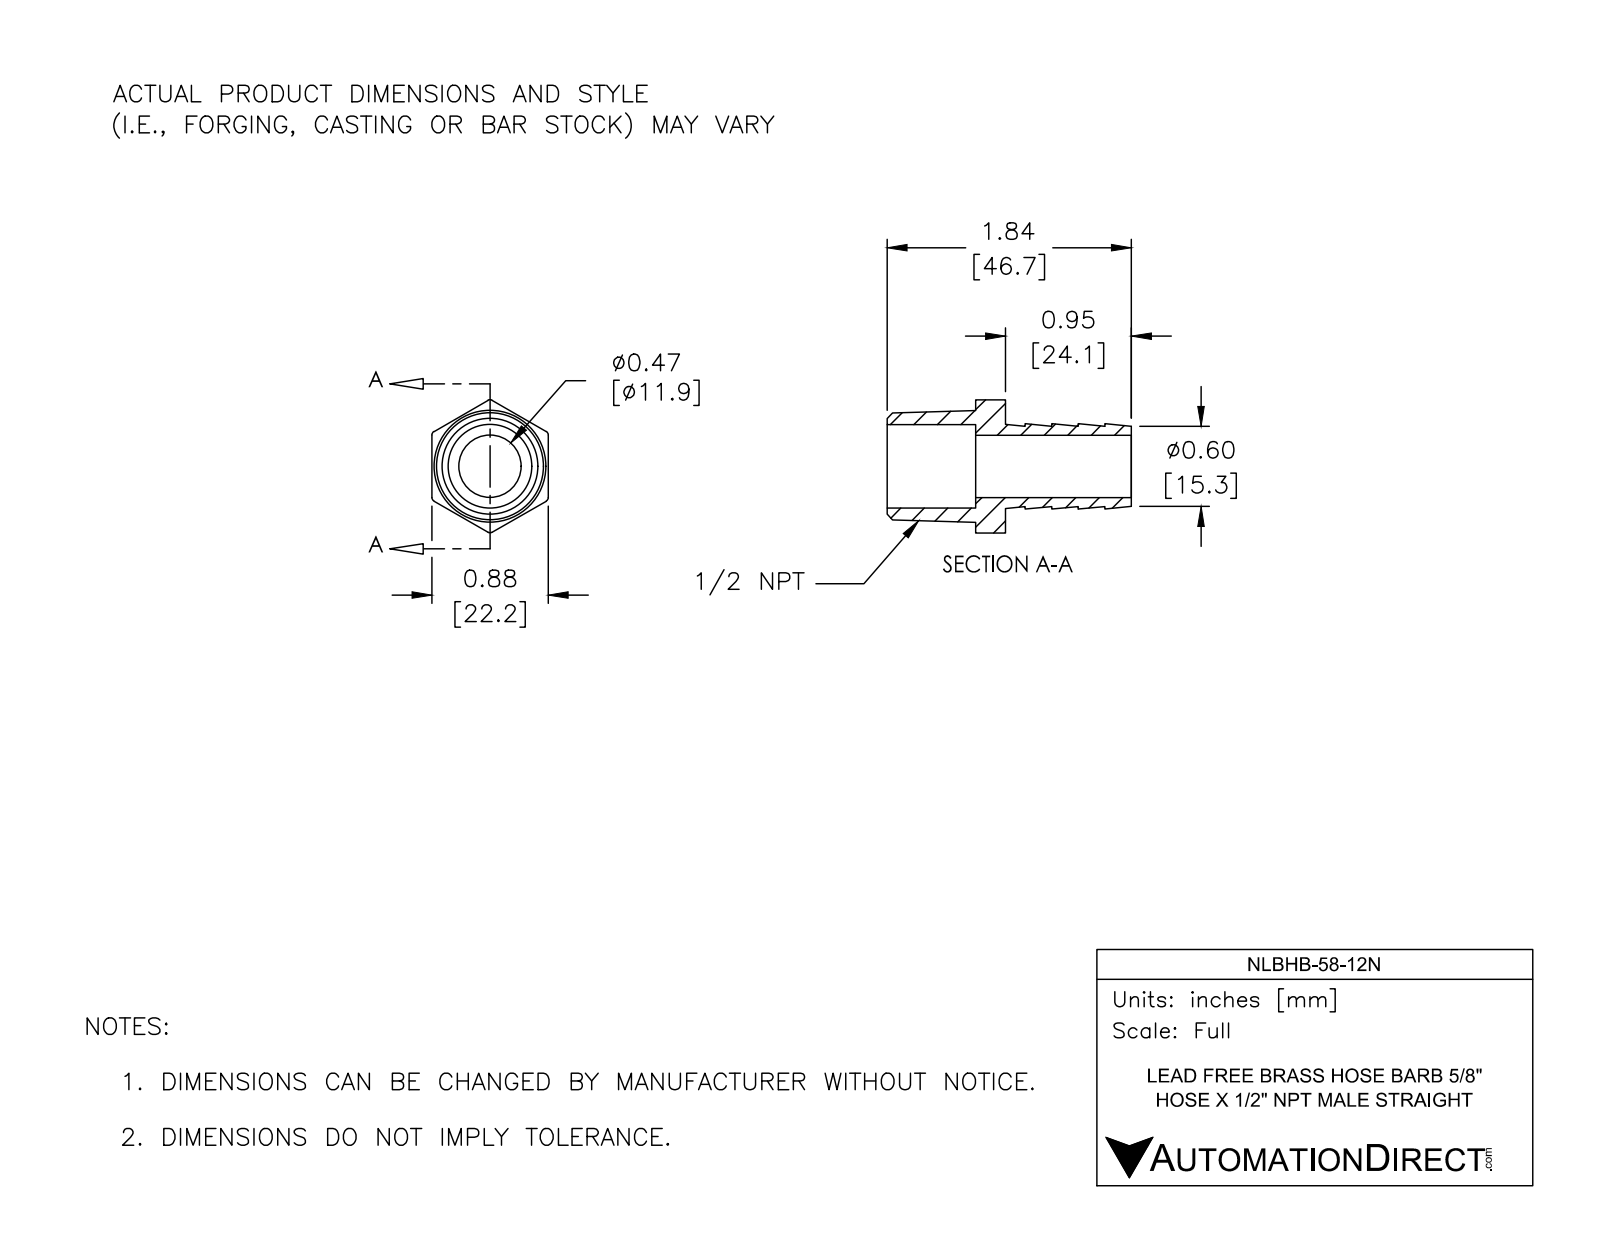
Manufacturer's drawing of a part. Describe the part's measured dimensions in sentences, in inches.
The part is named "NLBHB-58-12N". Its 3-D file was written by "SolidWorks 2017 (AUTOMOTIVE_DESIGN)". It is 1 solid with 39 faces: 15 planar, 10 cylindrical and 14 other. Overall it measures 1.838 by 1.001 by 0.875 inches. Its volume is 0.379 cubic inches and its surface area 8.286 square inches. Round holes: 1 of diameter 0.469, 1 of diameter 0.628. Partial cylindrical surfaces (rounded edges, fillets, slot ends): 6 of radius 0.03. The main face-to-face distances are 0.875, 0.223, 0.2, 0.948, 1.171, 0.4, 1.838, 0.89, 0.667, 0.6.
